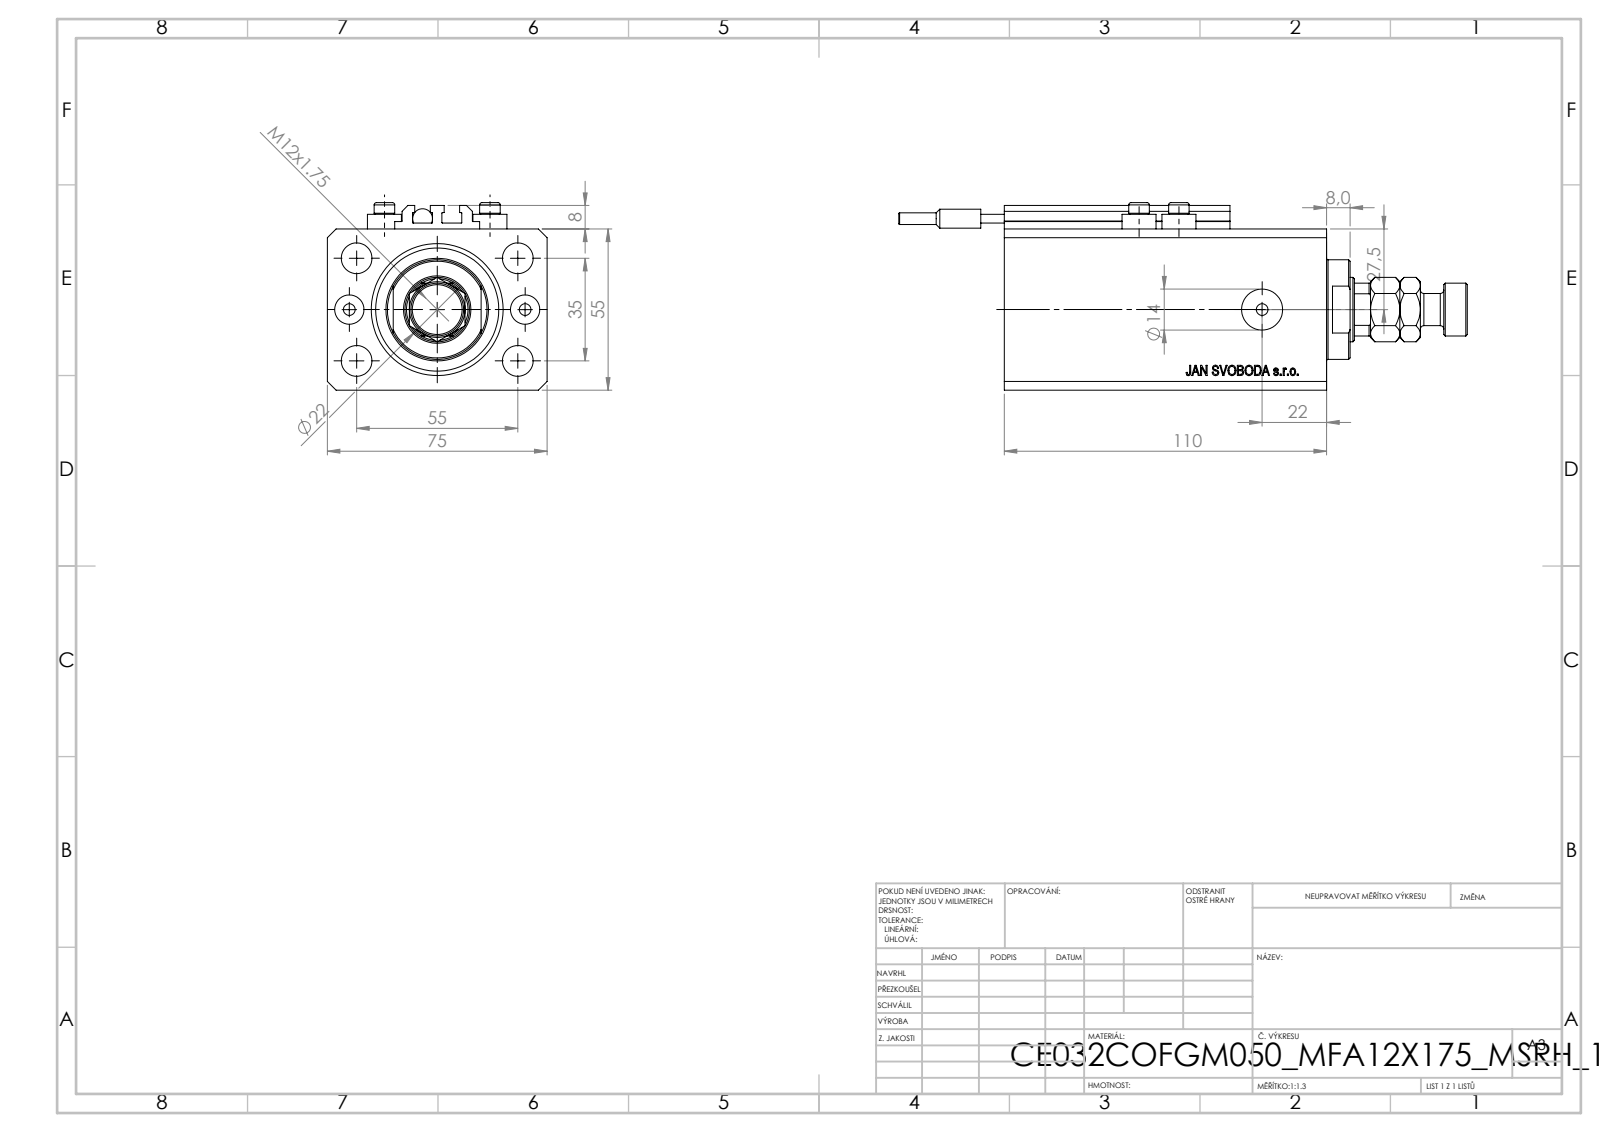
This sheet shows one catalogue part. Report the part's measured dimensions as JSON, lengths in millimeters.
{"part_name": "V250CE_VC_C; ALLEN BOLT V250CE; V250CE_C_VCP; SWITCH_V250CE (+2 more)", "step_written_by": "SolidWorks 2019 (CONFIG_CONTROL_DESIGN)", "units": "millimeters", "bodies": {"solids": 10, "faces": 1112, "planar": 536, "cylindrical": 96, "other": 480}, "overall_size": [194, 75, 64], "volume_mm3": 418785, "surface_area_mm2": 95189, "round_holes": [[4, 8], [10.5, 5], [10, 2], [14, 2], [22, 1], [32, 1], [45, 1]], "round_bosses_or_shafts": [[11.6, 4], [7, 4], [34, 1], [18, 1], [11, 1], [6.8, 1], [6.5, 1], [4, 1]], "partial_cylinders_radius": [[0.2, 10], [10.5, 1]], "face_to_face_distances": [55, 75, 15, 110, 95, 9.9, 85.1, 100.1, 2.5, 3], "hole_center_spacings": [17.68, 32.6, 60.1, 13.6, 30, 35, 36, 38.48]}
